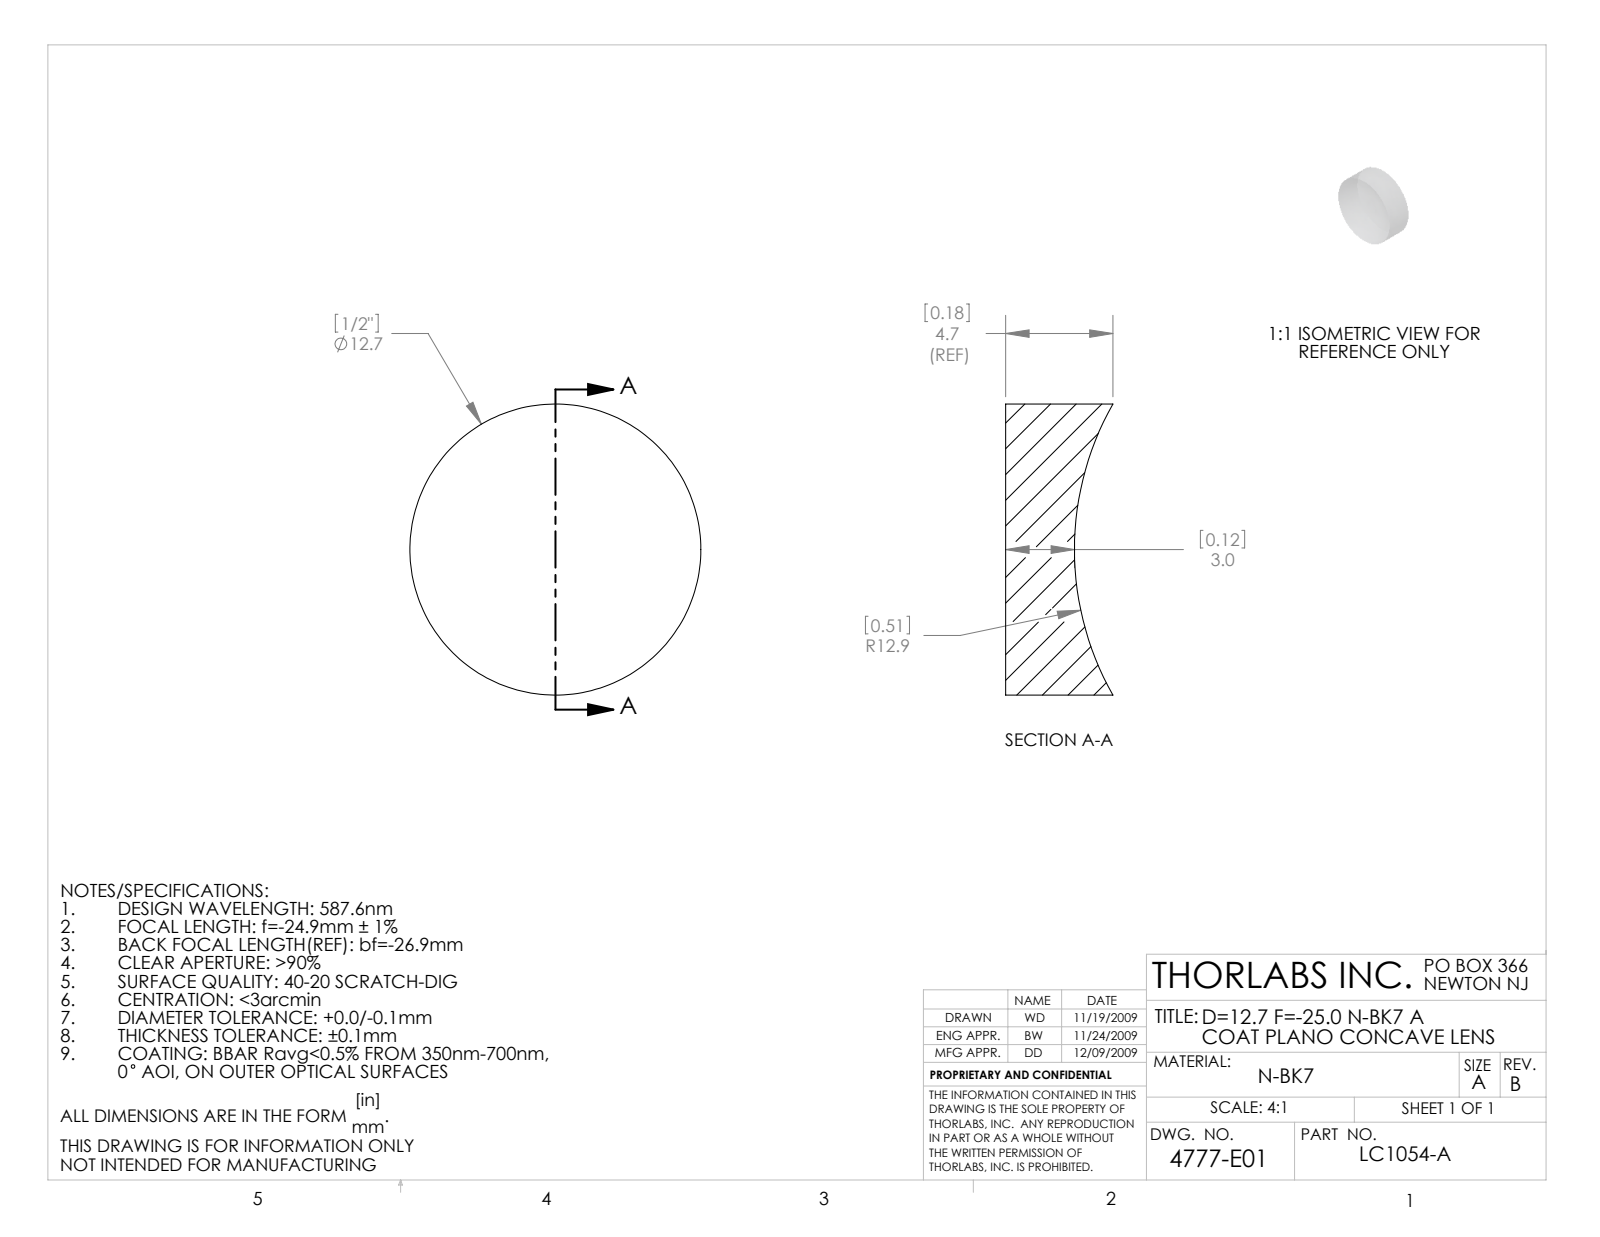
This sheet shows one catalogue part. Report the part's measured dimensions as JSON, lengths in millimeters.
{"part_name": "4777-E0W", "step_written_by": "SolidWorks 2009 (AUTOMOTIVE_DESIGN)", "units": "millimeters", "bodies": {"solids": 1, "faces": 5, "planar": 1, "cylindrical": 2, "other": 2}, "overall_size": [12.7, 12.7, 4.68], "volume_mm3": 484, "surface_area_mm2": 449, "round_bosses_or_shafts": [[12.7, 1]]}
